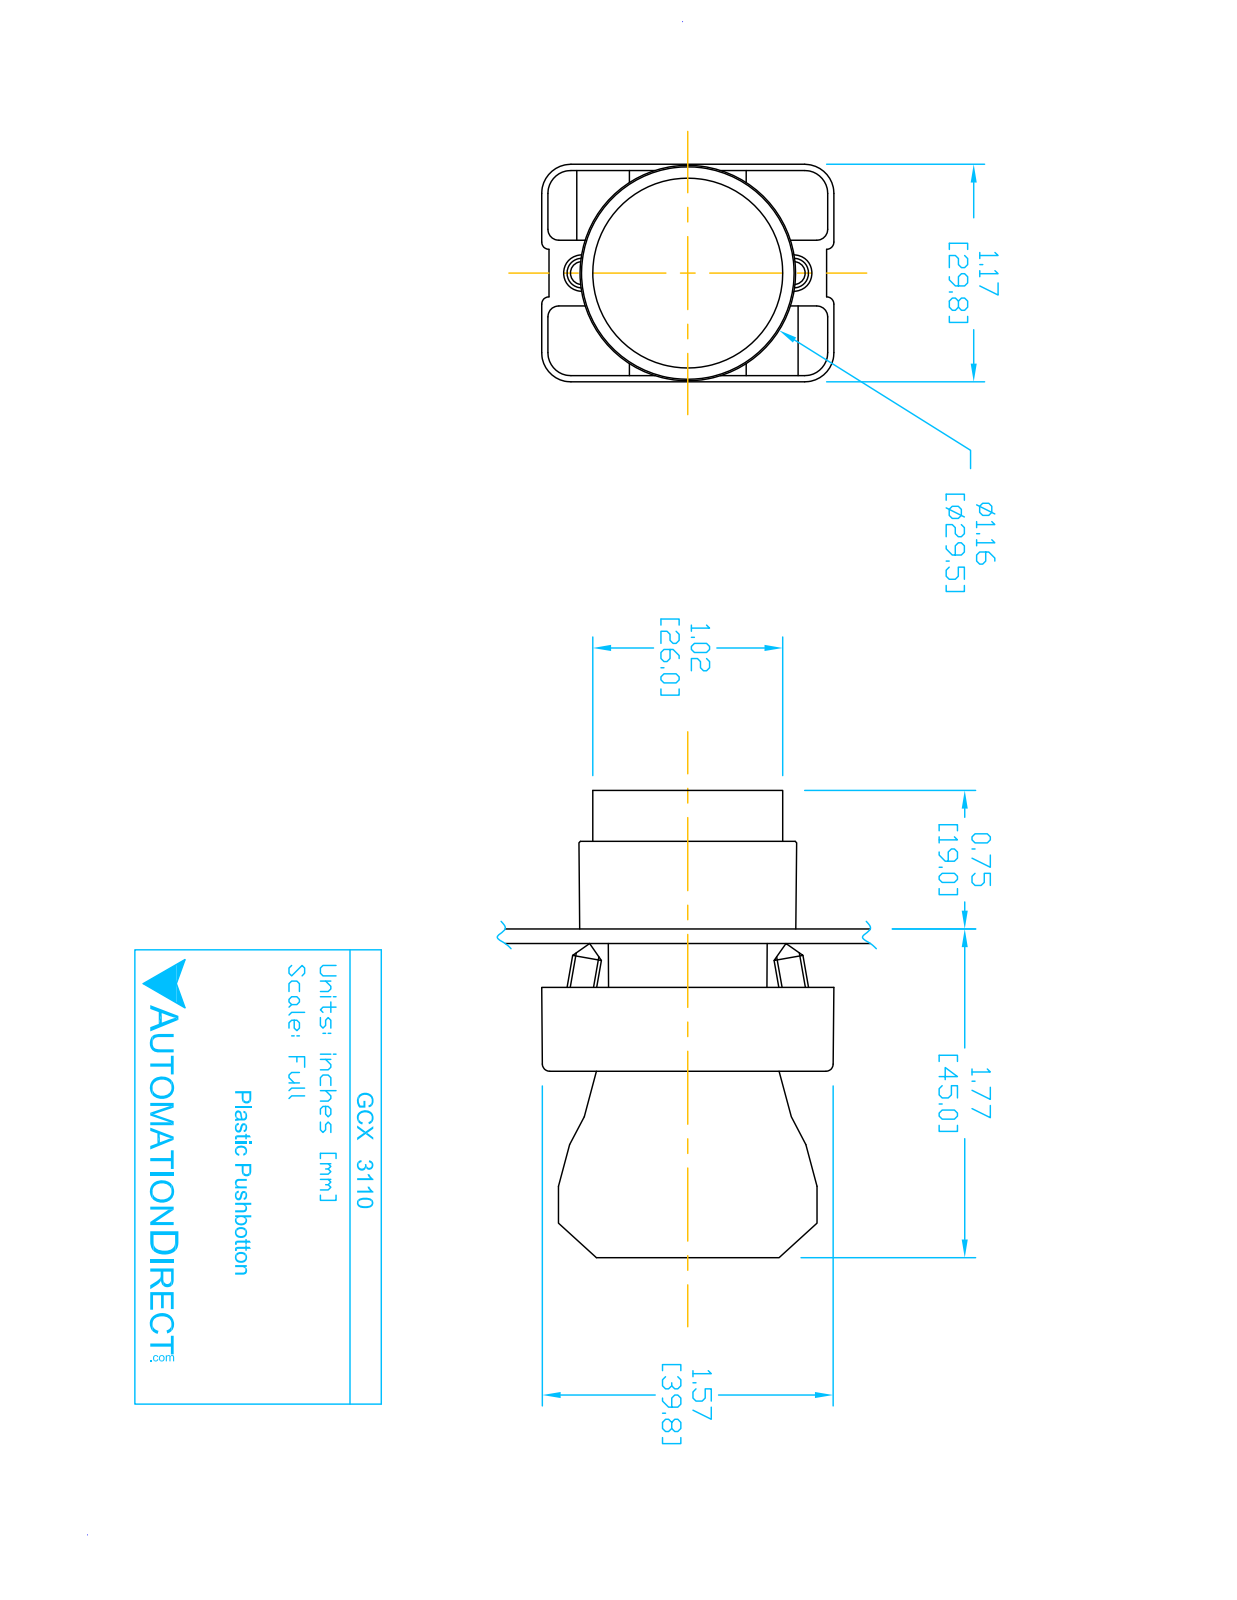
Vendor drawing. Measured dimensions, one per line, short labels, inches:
name: ECX3029-2; GCX3110; ecx1040; GCX3110 OPERATOR
written by: SolidWorks 2016 (AUTOMOTIVE_DESIGN)
unit: in
bodies: 6 solids, 383 faces (222 planar, 132 cylindrical, 29 other)
size: 2.492 × 1.581 × 1.177
volume: 1.584 in³; area: 26.47 in²
holes: 2× ⌀0.079, 2× ⌀0.124, 2× ⌀0.13, 1× ⌀0.087, 1× ⌀0.197, 1× ⌀0.878, 1× ⌀0.888, 1× ⌀1.024
bosses: 2× ⌀0.157, 1× ⌀1.175, 1× ⌀1.004, 1× ⌀0.945, 1× ⌀0.856, 1× ⌀0.78
rounds: 24× R0.059, 12× R0.041, 12× R0.124, 12× R0.157, 4× R0.039, 2× R0.128, 1× R0.02, 1× R0.063
face distances: 0.579, 0.033, 1.193, 0.031, 0.472, 0.72, 0.276, 0.689, 0.598, 1.161
hole spacings: 0.236, 0.544, 0.472, 0.49
